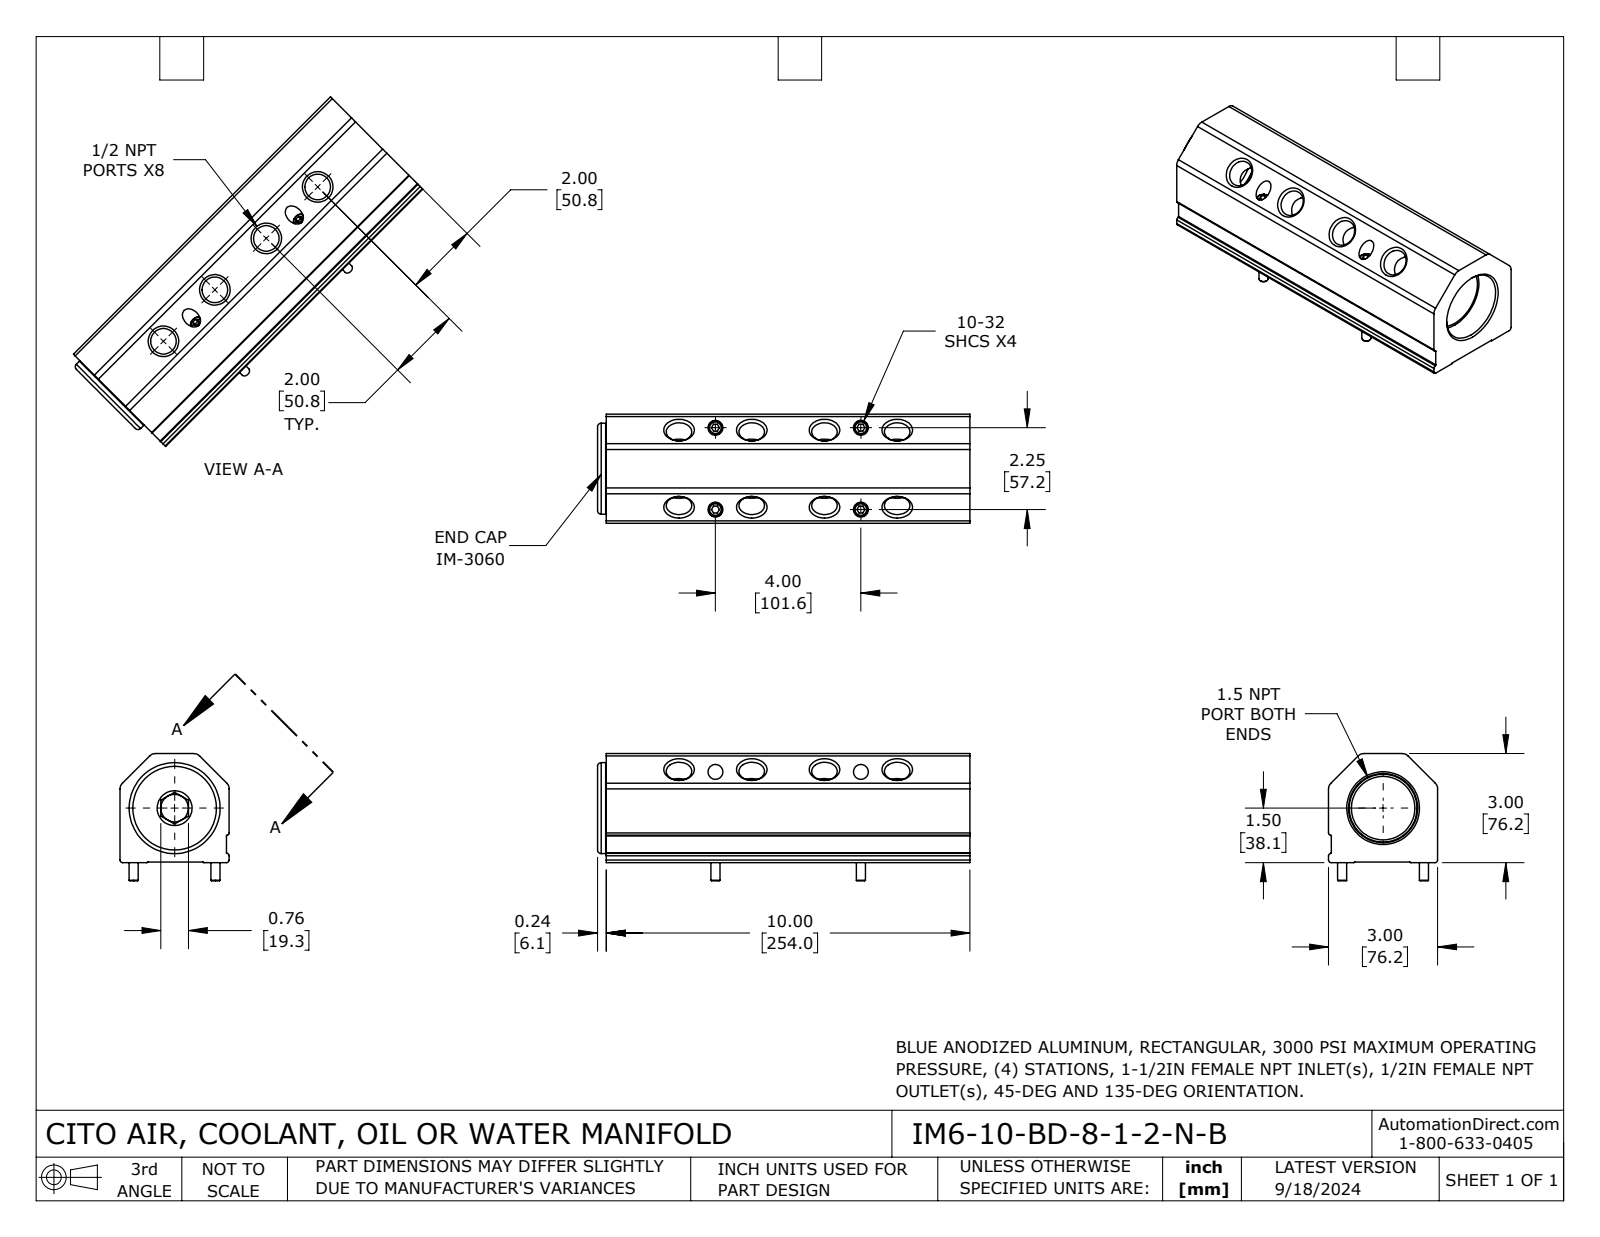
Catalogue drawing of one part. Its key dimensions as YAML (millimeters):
part_name: "IM6-10-BD-8-1-2-N-B"
step_written_by: "SolidWorks 2023 (CONFIG_CONTROL_DESIGN)"
units: millimeters
bodies: {solids: 6, faces: 210, planar: 76, cylindrical: 74, other: 60}
overall_size: [260.1, 88.9, 76.2]
volume: 936000
surface_area: 139900
round_holes:
  - {diameter: 17.9, count: 8}
  - {diameter: 6.8, count: 4}
  - {diameter: 10.3, count: 4}
  - {diameter: 19.3, count: 1}
  - {diameter: 44.3, count: 1}
  - {diameter: 57.5, count: 1}
round_bosses_or_shafts:
  - {diameter: 9.5, count: 4}
  - {diameter: 6.4, count: 4}
  - {diameter: 63.5, count: 1}
  - {diameter: 50.4, count: 1}
  - {diameter: 44.7, count: 1}
partial_cylinders:
  - {radius: 0.5, count: 6}
  - {radius: 5.7, count: 4}
  - {radius: 1.6, count: 2}
  - {radius: 1.9, count: 2}
face_to_face_distances: [76.2, 0.5, 75.7, 254, 1.9, 74.3, 6.1, 260.1, 19.4, 13.3]
hole_center_spacings: [50.8, 101.6, 57.2, 116.6, 152.4]
